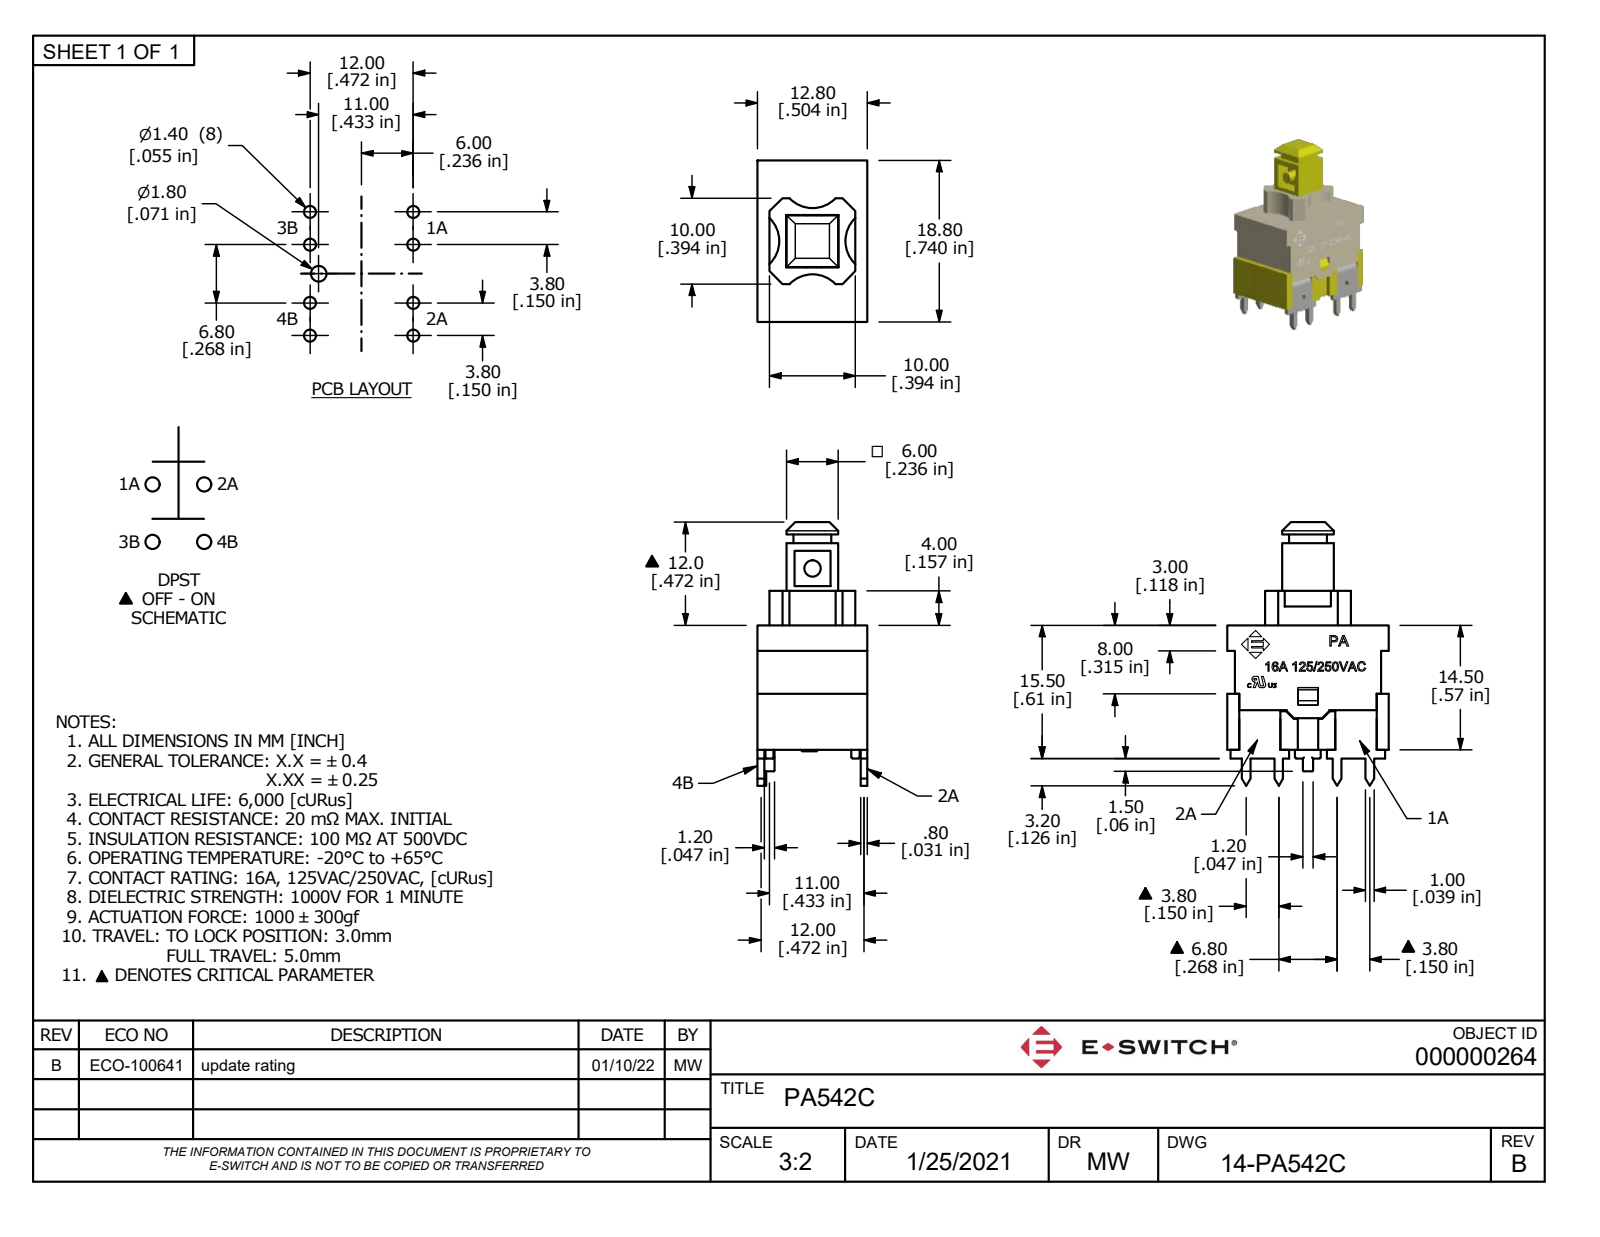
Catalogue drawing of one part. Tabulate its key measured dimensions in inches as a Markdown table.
| quantity | value |
| --- | --- |
| part name | PA542C |
| STEP written by | Autodesk Inventor 2022 (AUTOMOTIVE_DESIGN) |
| units | inches |
| bodies | 1 solid, 1259 faces (938 planar, 121 cylindrical, 200 other) |
| overall size | 1.222 × 0.835 × 0.587 |
| volume | 0.159 in³ |
| surface area | 9.271 in² |
| round holes (diameter × count) | 0.039 × 2, 0.055 × 2, 0.118 × 1, 0.157 × 1 |
| round bosses / shafts (diameter × count) | 0.037 × 4, 0.098 × 2, 0.197 × 1 |
| partial cylindrical surfaces (radius × count) | 0.01 × 27, 0.005 × 16, 0.059 × 12, 0.006 × 8, 0.02 × 5, 0.031 × 4, 0.039 × 4, 0.011 × 3 |
| main face-to-face distances | 0.031, 0.026, 0.024, 0.035, 0.447, 0.043, 0.045, 0.39, 0.504, 0.057 |
| hole center spacings | 0.148, 0.228, 0.441 |
